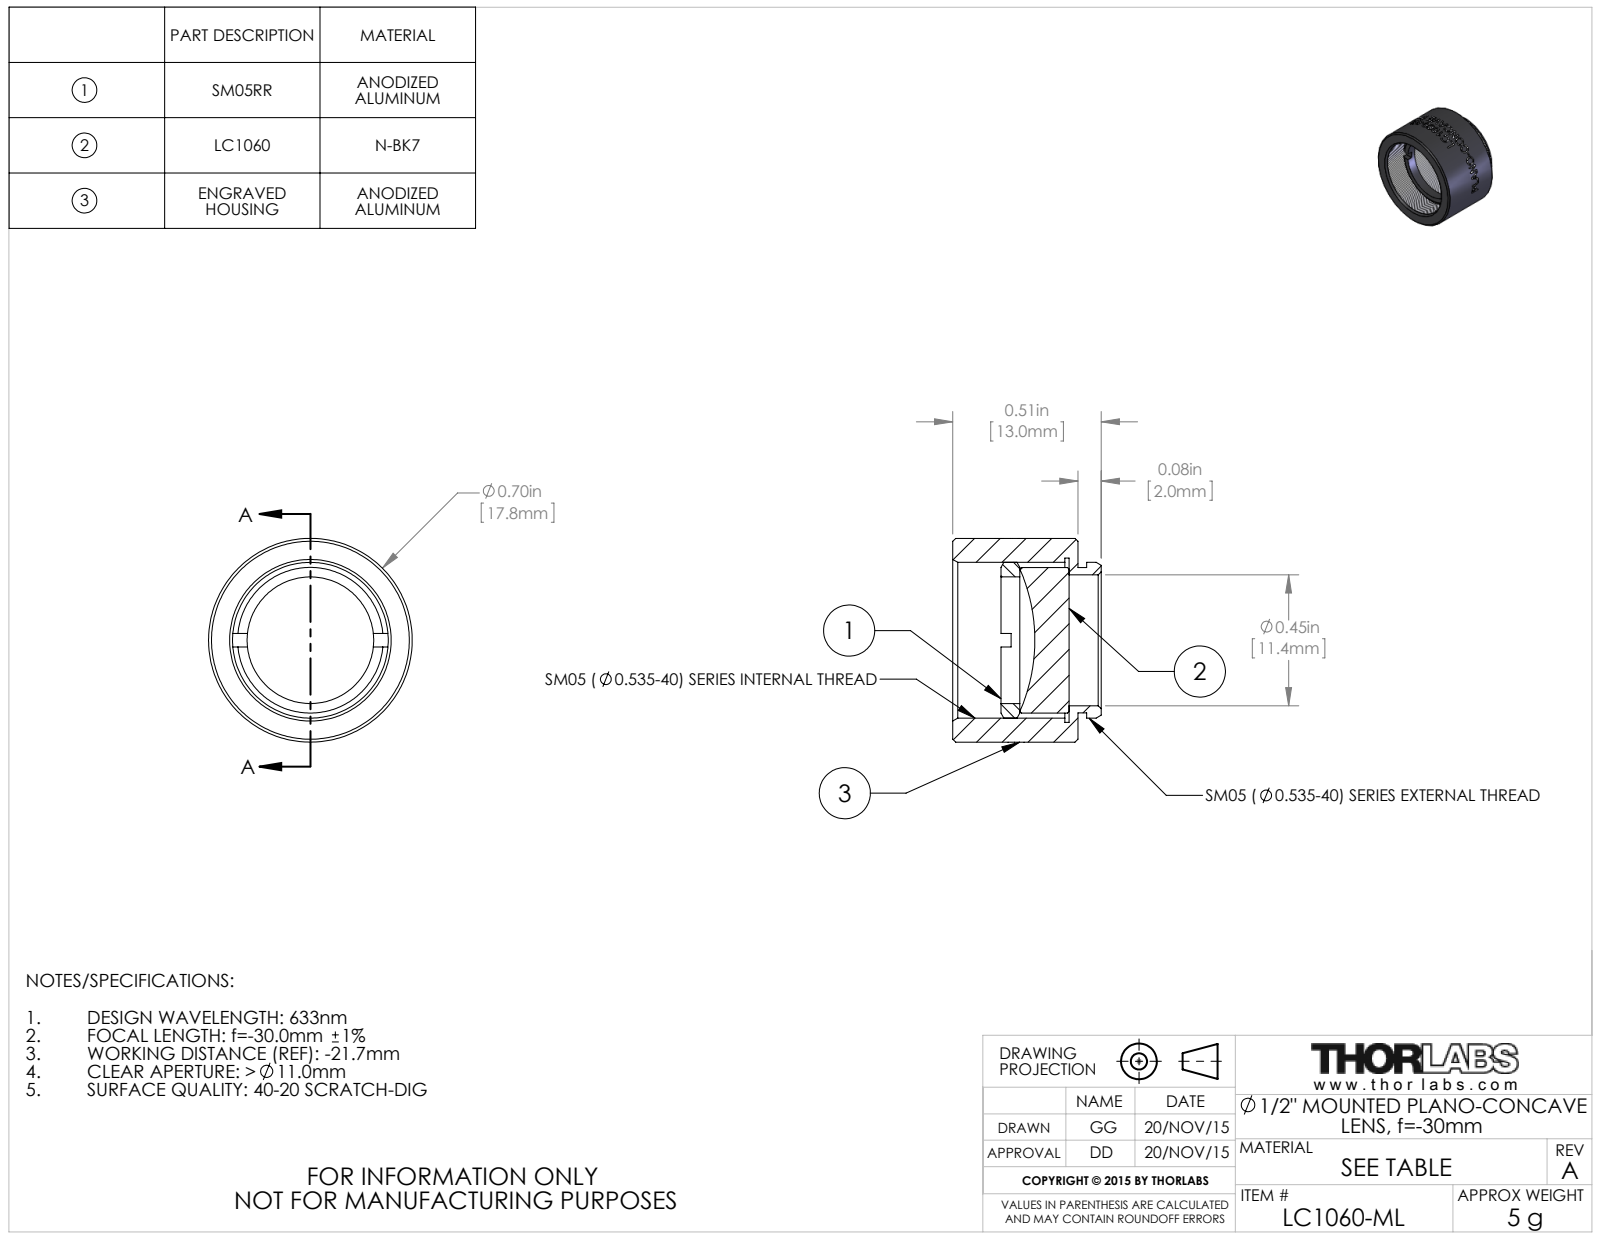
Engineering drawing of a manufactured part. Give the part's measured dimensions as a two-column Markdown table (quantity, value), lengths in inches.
| quantity | value |
| --- | --- |
| part name | TTN045245-E0W |
| STEP written by | SolidWorks 2014 (CONFIG_CONTROL_DESIGN) |
| units | inches |
| bodies | 3 solids, 115 faces (16 planar, 78 cylindrical, 21 other) |
| overall size | 0.7 × 0.7 × 0.51 |
| volume | 0.107 in³ |
| surface area | 3.392 in² |
| round holes (diameter × count) | 0.435 × 1, 0.45 × 1, 0.535 × 1, 0.565 × 1 |
| round bosses / shafts (diameter × count) | 0.7 × 1, 0.535 × 1, 0.5 × 1, 0.499 × 1 |
| main face-to-face distances | 0.03, 0.43, 0.4, 0.2, 0.169, 0.231, 0.265, 0.234, 0.065, 0.166 |
